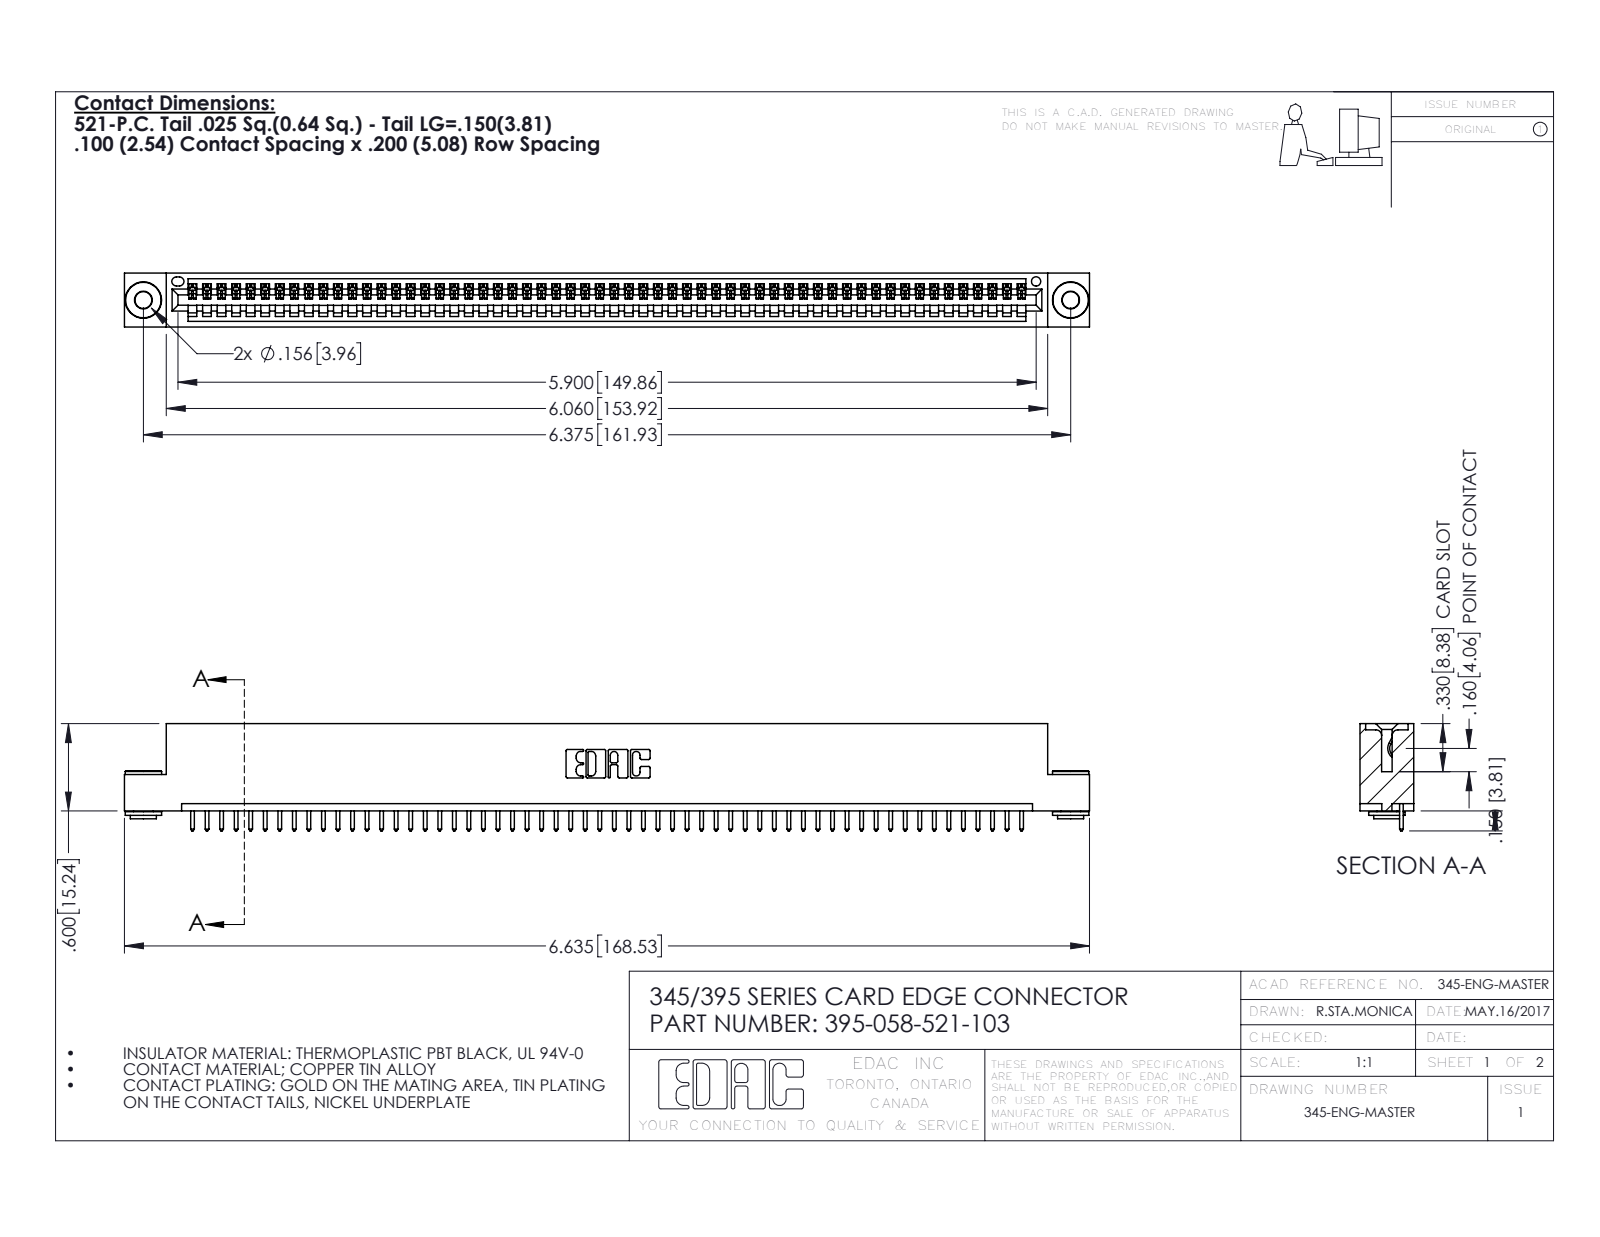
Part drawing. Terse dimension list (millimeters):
name: 345 Part_Flush Mounting Lugs - 0.156 Dia-TH; 345-292-001_345-293-121; 345-250-002_345-250-002-102; 395-058-521-103
written by: SolidWorks 2016 (CONFIG_CONTROL_DESIGN)
unit: mm
bodies: 61 solids, 3528 faces (2410 planar, 1110 cylindrical, 8 other)
size: 168.5 × 18.7 × 9.4
volume: 16 000 mm³; area: 21 040 mm²
holes: 2× ⌀2.9, 2× ⌀4, 1× ⌀1.6
bosses: 2× ⌀6.4, 2× ⌀4.6, 2× ⌀3.5
rounds: 116× R0.2, 116× R0.3, 22× R0.3, 6× R0.2, 6× R0.8, 3× R0.7, 2× R0.8, 2× R1
face distances: 1.8, 7.6, 9.4, 5.1, 0.6, 2.5, 6.9, 5.7, 3.8, 1.8
hole spacings: 6.9, 155.9, 161.9
